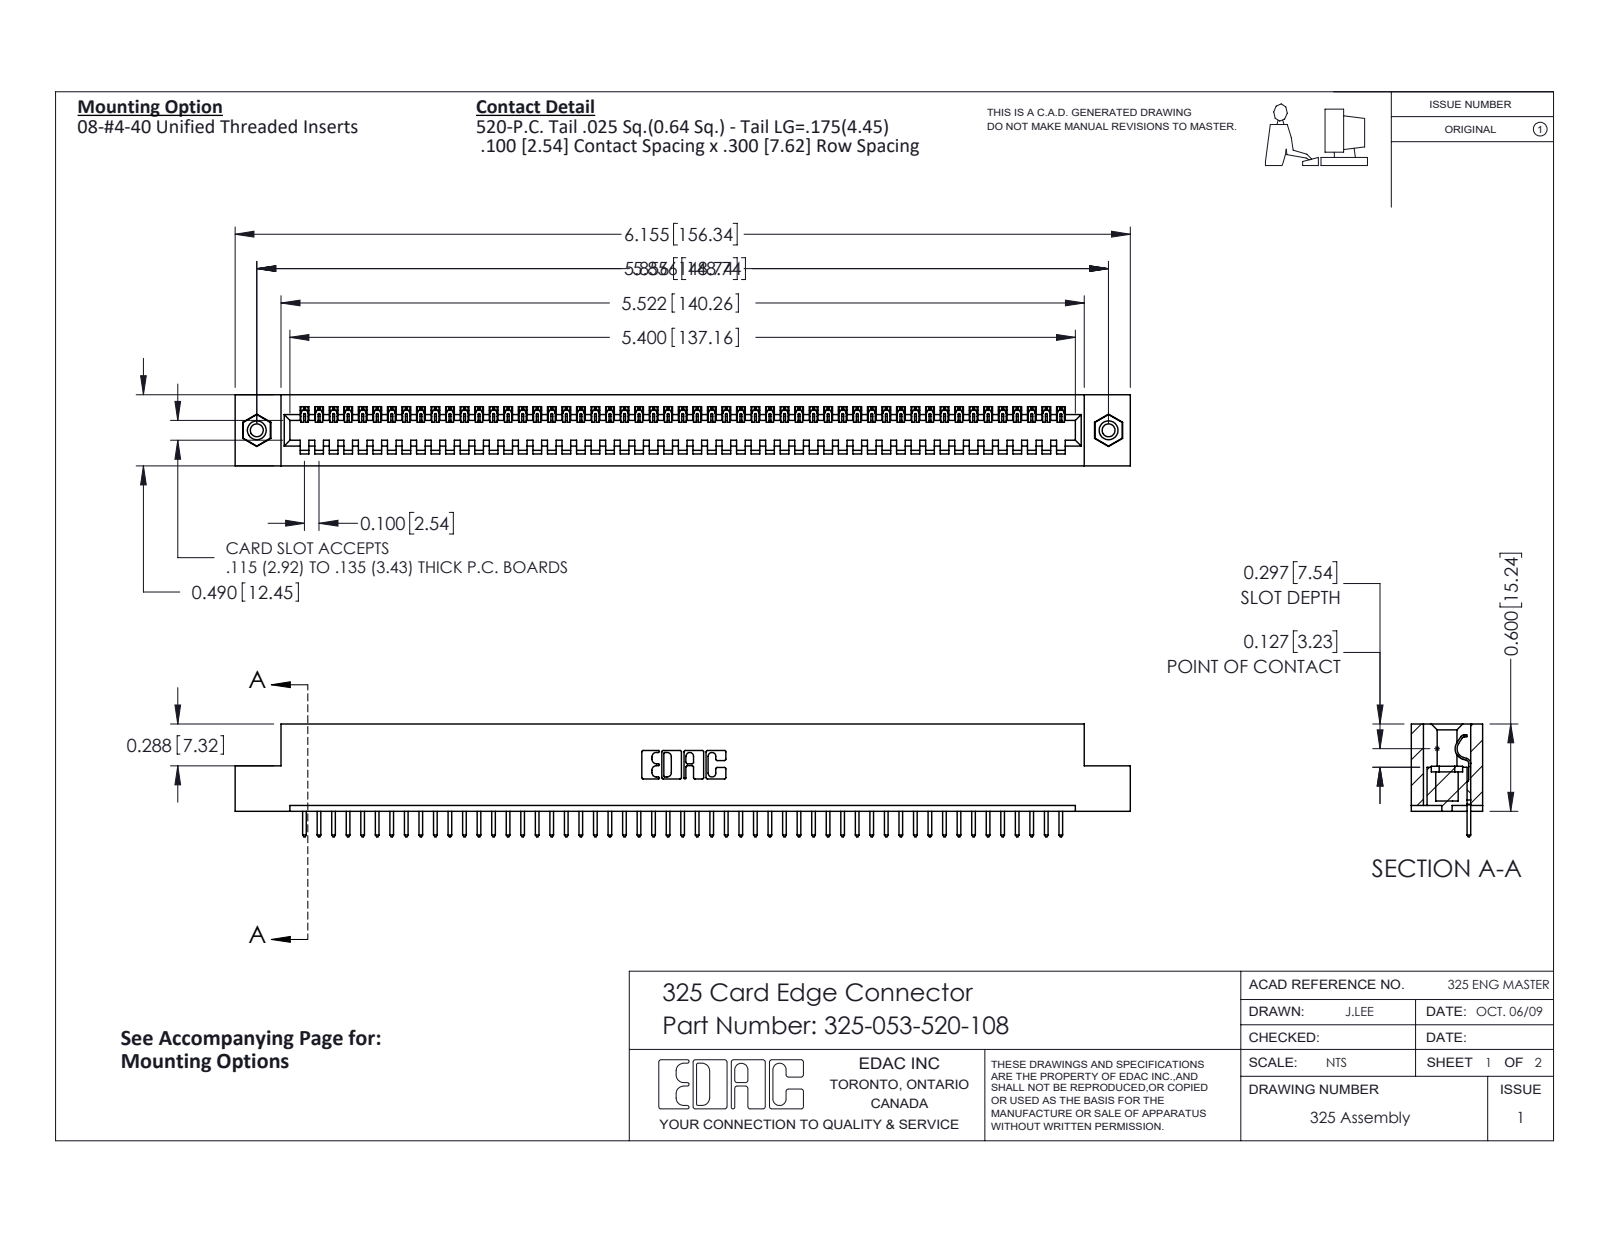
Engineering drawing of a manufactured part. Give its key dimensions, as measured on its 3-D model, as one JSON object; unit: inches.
{"part_name": "325-292-001_325-293-120; 345-250-001_345-250-003-102; 325 Part_TI; 325-053-520-108", "step_written_by": "SolidWorks 2016 (CONFIG_CONTROL_DESIGN)", "units": "inches", "bodies": {"solids": 56, "faces": 3248, "planar": 2328, "cylindrical": 904, "other": 16}, "overall_size": [6.155, 0.775, 0.49], "volume_in3": 1.208, "surface_area_in2": 32.96, "round_holes": [[0.089, 2], [0.125, 2], [0.16, 2]], "round_bosses_or_shafts": [[0.155, 2]], "partial_cylinders_radius": [[0.006, 106], [0.01, 106], [0.01, 22], [0.007, 6], [0.031, 6], [0.026, 3], [0.014, 1], [0.022, 1]], "face_to_face_distances": [0.083, 0.407, 0.49, 0.3, 0.107, 0.383, 0.025, 0.325, 0.263, 0.56], "hole_center_spacings": [5.856]}
